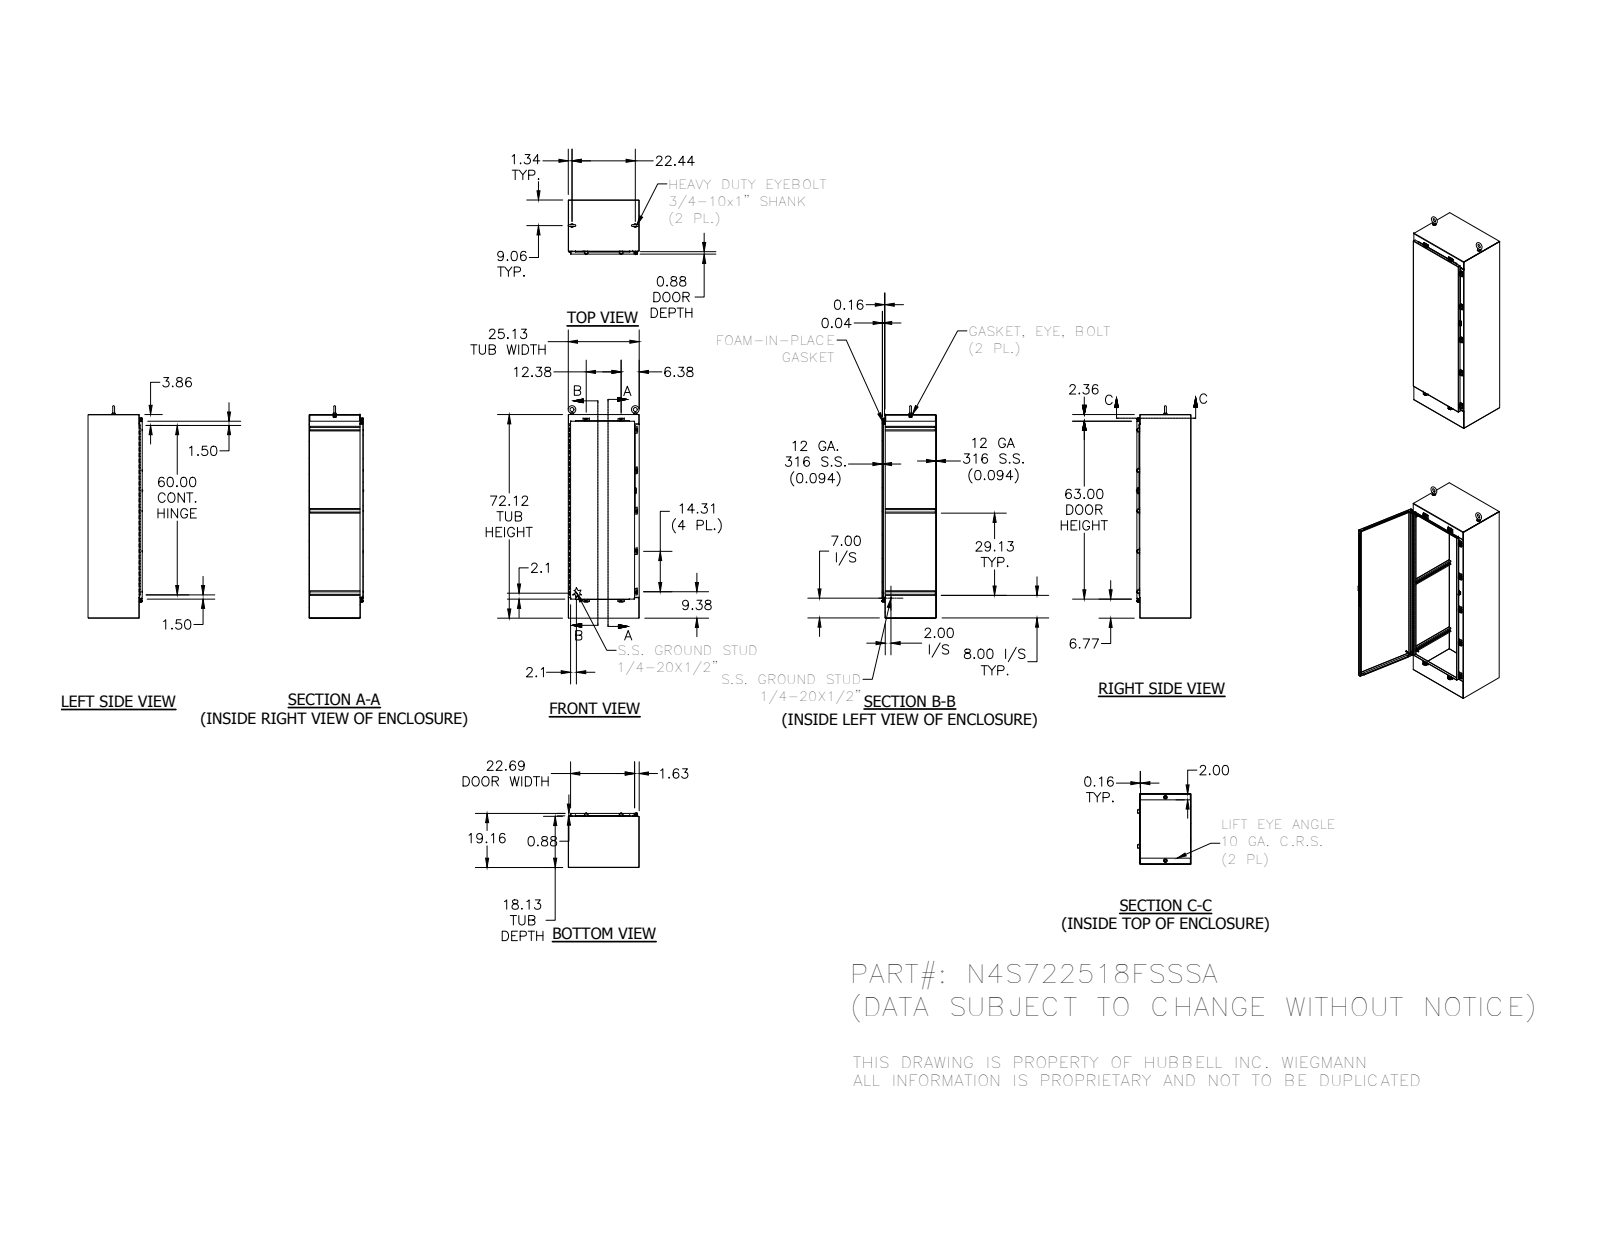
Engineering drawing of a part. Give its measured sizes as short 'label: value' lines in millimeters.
name: 30824-1_1; N4S722518FSSSATOP_1; N4S722518FSSSABTM_1; 38413_1 (+8 more)
written by: SolidWorks 2014 (AUTOMOTIVE_DESIGN)
unit: mm
bodies: 78 solids, 3000 faces (1210 planar, 1210 cylindrical, 580 other)
size: 1911.3 × 638.2 × 491.6
volume: 14 080 000 mm³; area: 11 380 000 mm²
holes: 9× ⌀5.4, 9× ⌀7.1, 9× ⌀7.6, 3× ⌀2.8, 2× ⌀16.3, 2× ⌀20.7, 1× ⌀3.2, 1× ⌀4, 1× ⌀12.7
bosses: 12× ⌀6.4, 9× ⌀13.2, 9× ⌀12.7, 9× ⌀8.9, 2× ⌀31.8, 2× ⌀28.4, 2× ⌀19.1, 2× ⌀8.6
rounds: 107× R0.8, 43× R3.2, 22× R1.6, 21× R6.4, 19× R0.8, 18× R0.5, 18× R1.3, 18× R2.2
face distances: 2.4, 484.3, 635.8, 481.9, 486.7, 633.4, 638.2, 458, 26.3, 1829.6
hole spacings: 363.6, 727.1, 20, 314.5, 1090.7, 1635.1, 1665.1, 11.4
